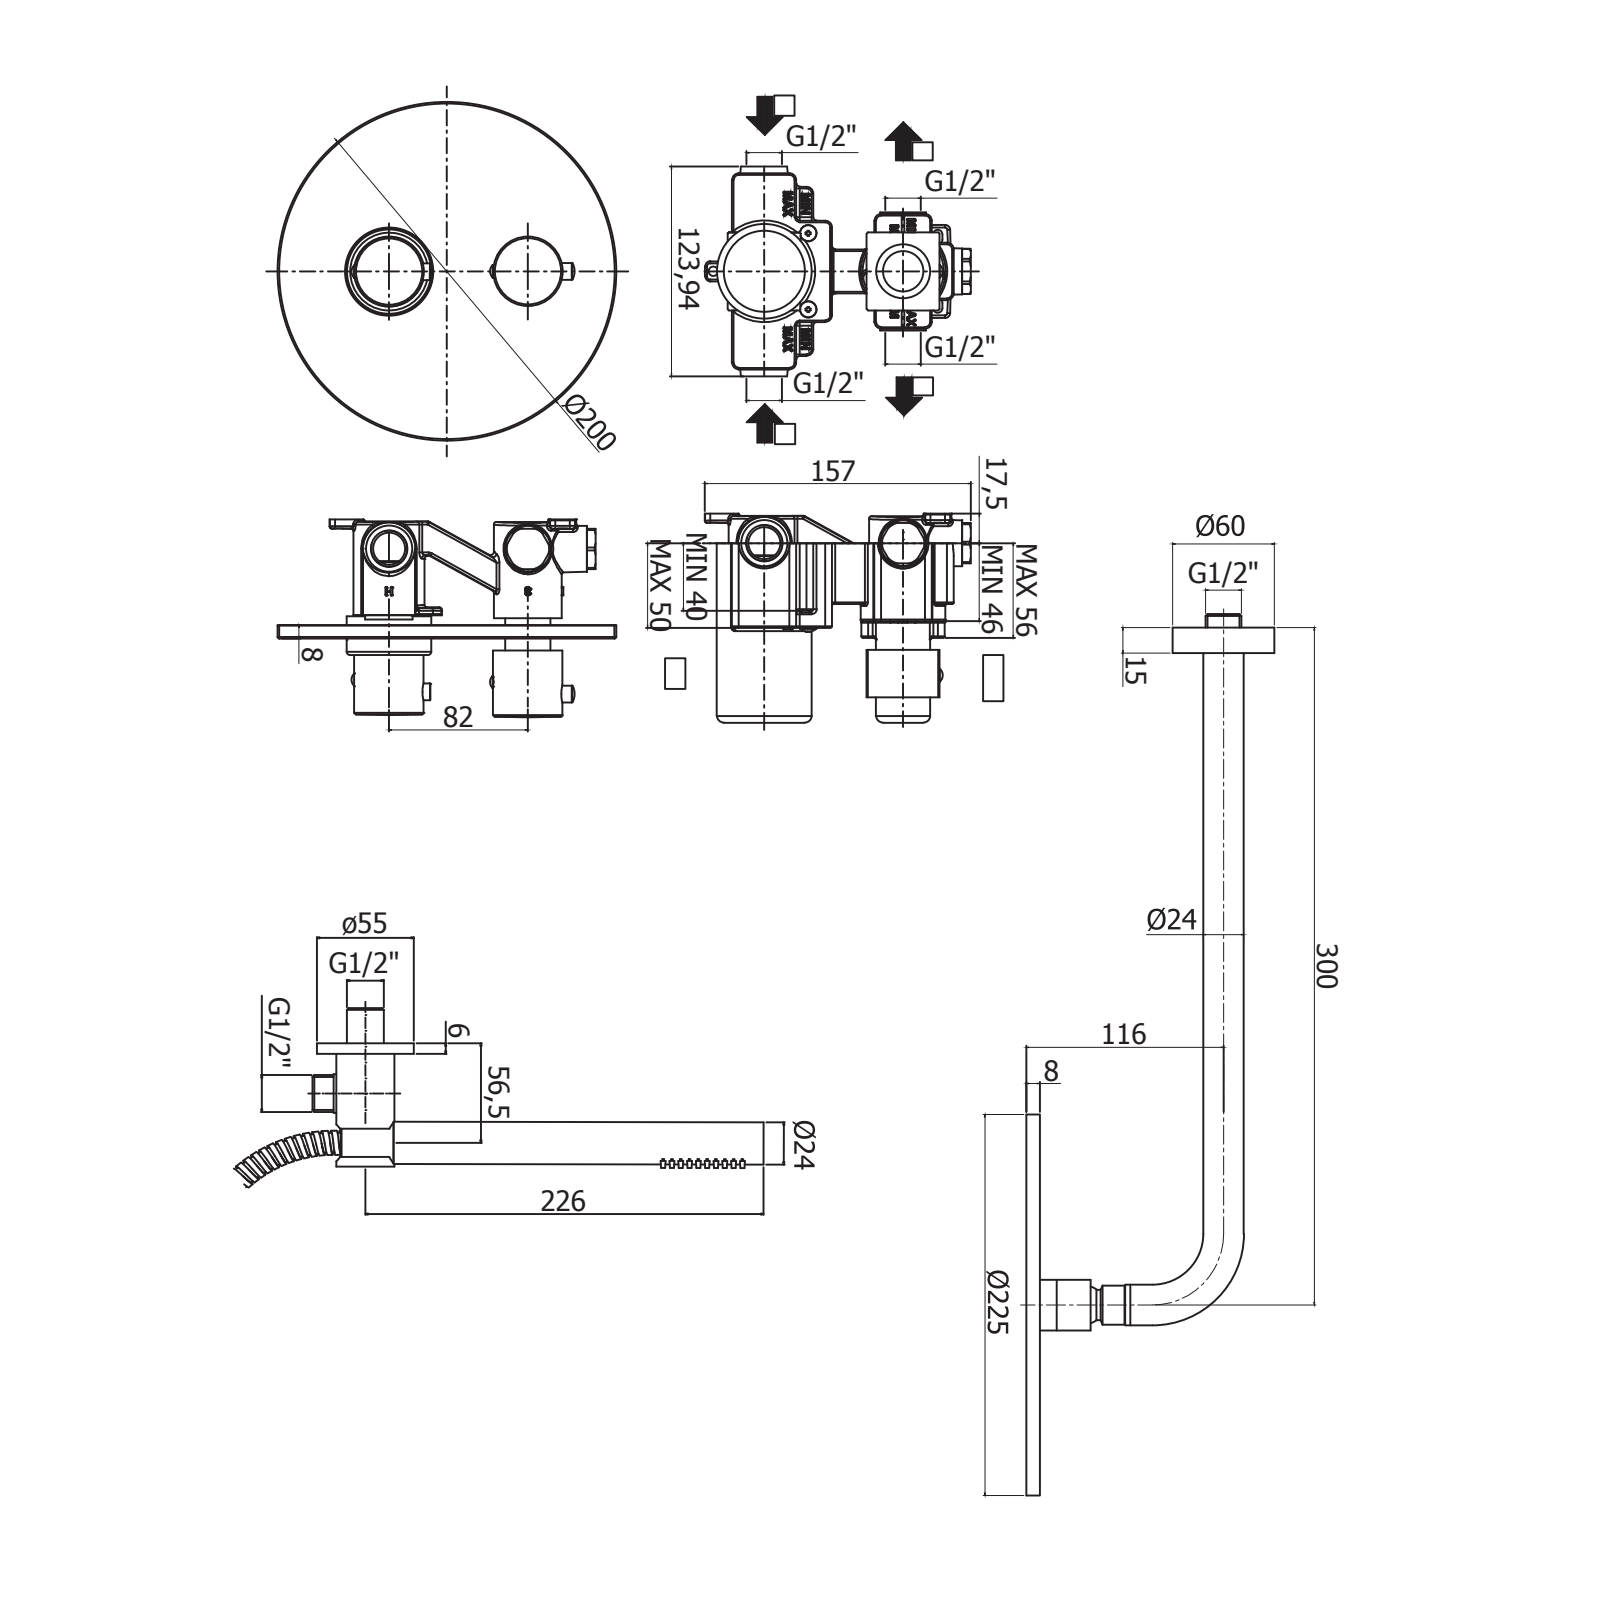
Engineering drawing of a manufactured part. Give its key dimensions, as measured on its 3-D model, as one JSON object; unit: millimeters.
{"part_name": "KITLIQ018CR", "step_written_by": "CREO PARAMETRIC BY PTC INC, 2020044 (CONFIG_CONTROL_DESIGN)", "units": "millimeters", "bodies": {"solids": 9, "faces": 5428, "planar": 1586, "cylindrical": 1710, "other": 2132}, "overall_size": [1095.7, 396.5, 390], "volume_mm3": 613152, "surface_area_mm2": 436207, "round_holes": [[2, 103], [4.5, 102], [1, 48], [8, 10], [3.25, 2], [4, 2], [4.2, 2], [5.5, 2], [6, 2], [6.4, 2], [10.1, 2], [10.5, 2]], "round_bosses_or_shafts": [[4, 190], [6, 11], [7, 10], [24, 4], [1.3, 4], [41, 3], [20, 3], [20.6, 2]], "partial_cylinders_radius": [[0.5, 92], [1, 33], [0.2, 30], [0.12, 24], [2, 21], [9, 11], [5.5, 10], [0.8, 6]], "face_to_face_distances": [1, 7.3, 8.3, 4.7, 5.7, 2.6, 8, 7, 1.5, 0.5], "hole_center_spacings": [10.97, 20.5, 10, 13.45, 4.5, 30.34, 20, 21.93]}
